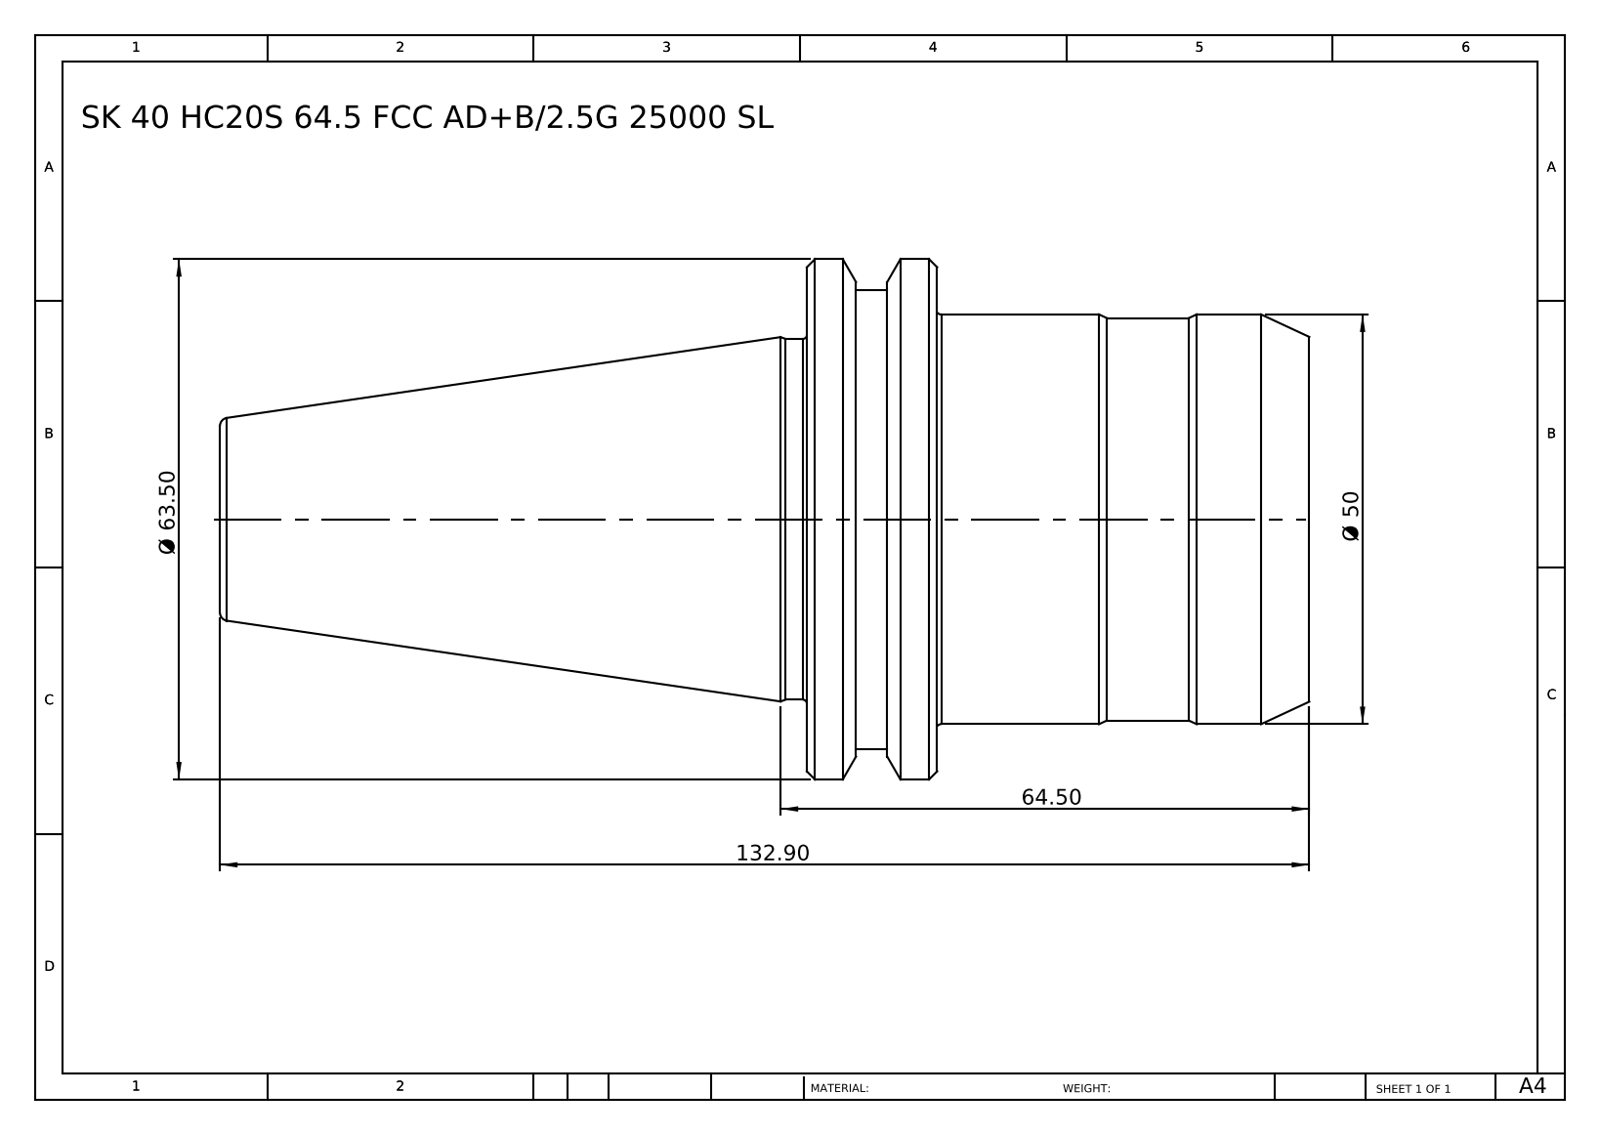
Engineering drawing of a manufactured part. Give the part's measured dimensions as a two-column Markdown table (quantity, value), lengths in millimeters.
| quantity | value |
| --- | --- |
| part name | SK 40 HC20S 64.5 FCC AD+B -2.5G 25000 SL |
| STEP written by | SolidWorks 2014 (CONFIG_CONTROL_DESIGN) |
| units | millimeters |
| bodies | 1 solid, 46 faces (6 planar, 14 cylindrical, 26 other) |
| overall size | 132.9 × 63.5 × 63.5 |
| volume | 204 253 mm³ |
| surface area | 23 677 mm² |
| round bosses / shafts (diameter × count) | 63.5 × 1, 56 × 1, 50 × 1, 49.1 × 1, 44 × 1 |
| main face-to-face distances | 61.3, 45.4, 15.9, 132.9, 87.5, 71.6, 51.5, 6.1, 9.8, 81.4 |
